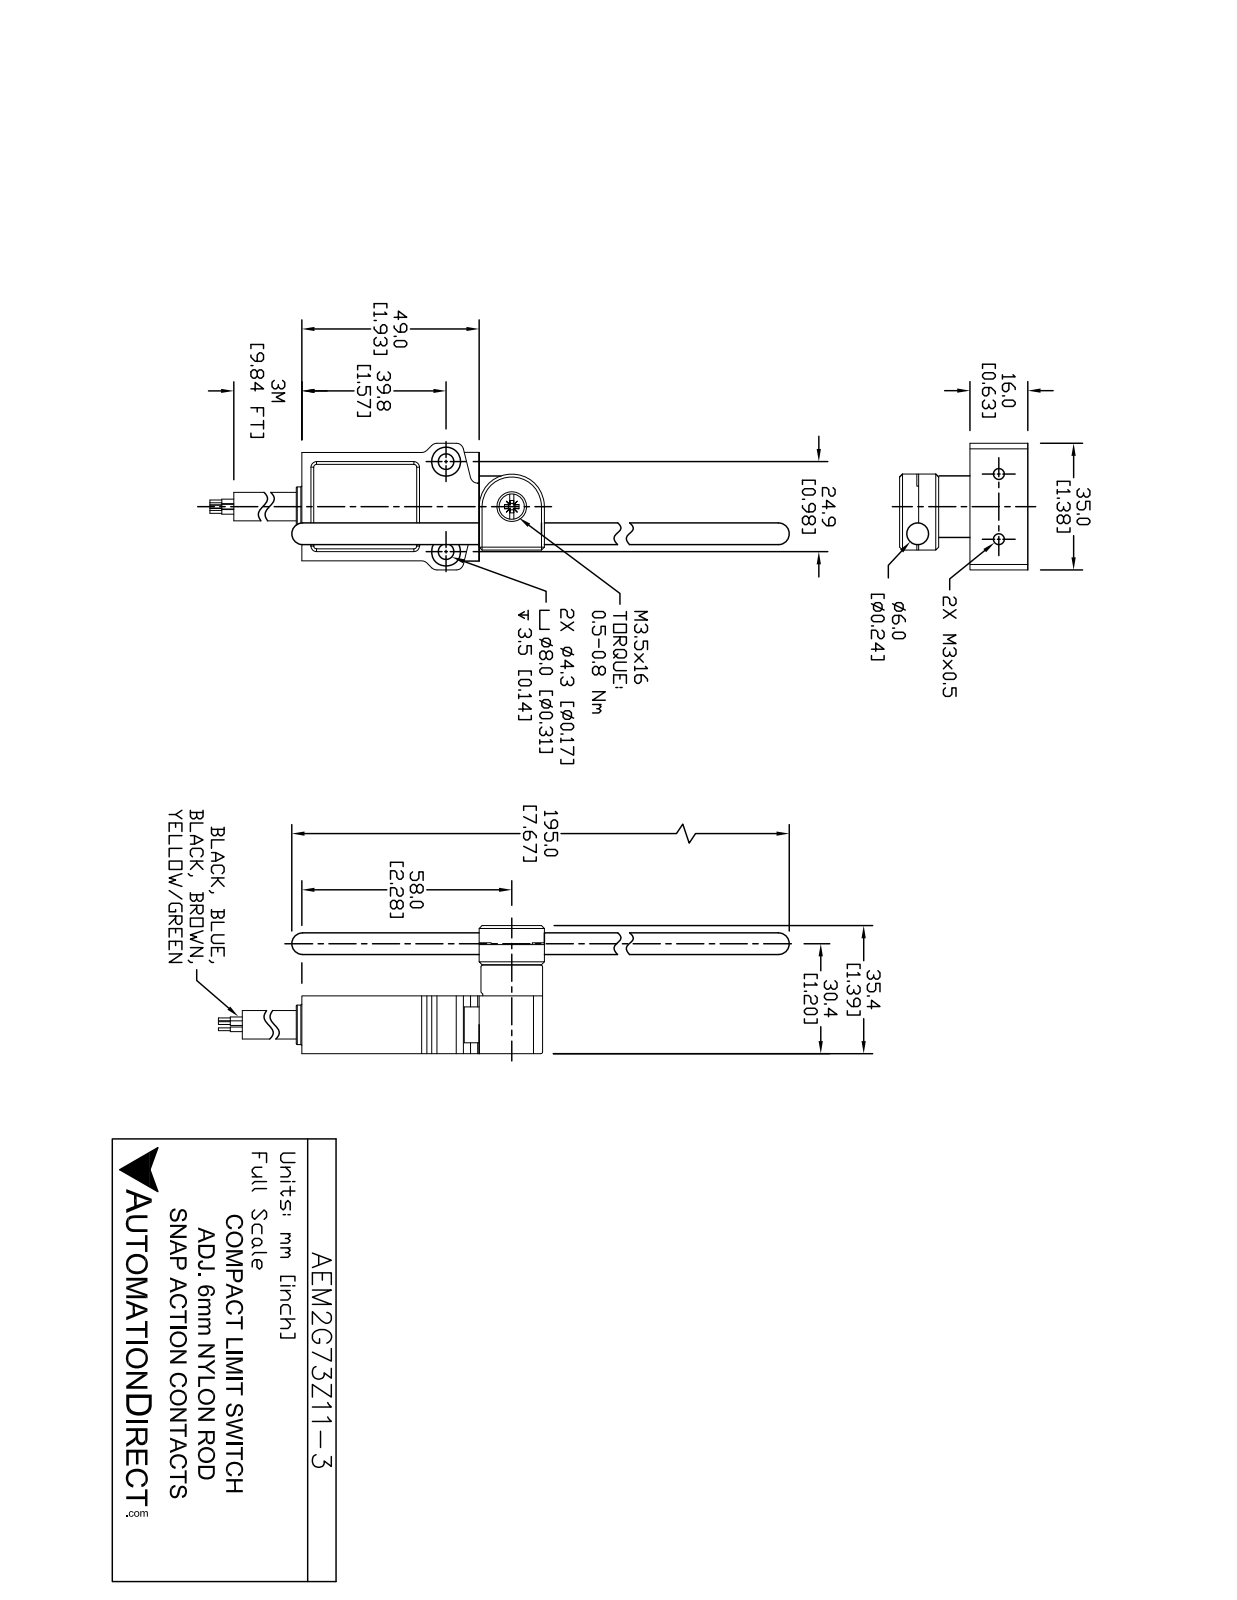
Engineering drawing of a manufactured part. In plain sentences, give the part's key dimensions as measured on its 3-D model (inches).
The part is named "AEM2G73Z11-3_Default". Its 3-D file was written by "SolidWorks 2021 (CONFIG_CONTROL_DESIGN)". It is 3 solids with 134 faces: 82 planar, 42 cylindrical and 10 other. Overall it measures 8.178 by 1.414 by 1.378 inches. Its volume is 2.245 cubic inches and its surface area 21.65 square inches. Round holes: 2 of diameter 0.118, 2 of diameter 0.173, 2 of diameter 0.323, 1 of diameter 0.197, 1 of diameter 0.32. Round bosses or shafts: 1 of diameter 0.622, 1 of diameter 0.289, 1 of diameter 0.276, 1 of diameter 0.24. Partial cylindrical surfaces (rounded edges, fillets, slot ends): 8 of radius 0.079, 1 of radius 0.256, 1 of radius 0.355. The main face-to-face distances are 0.63, 1.181, 0.354, 0.215, 1.929, 0.984, 0.28, 0.902, 0.472, 0.43. The hole center spacings are 0.863, 0.748, 0.984.
